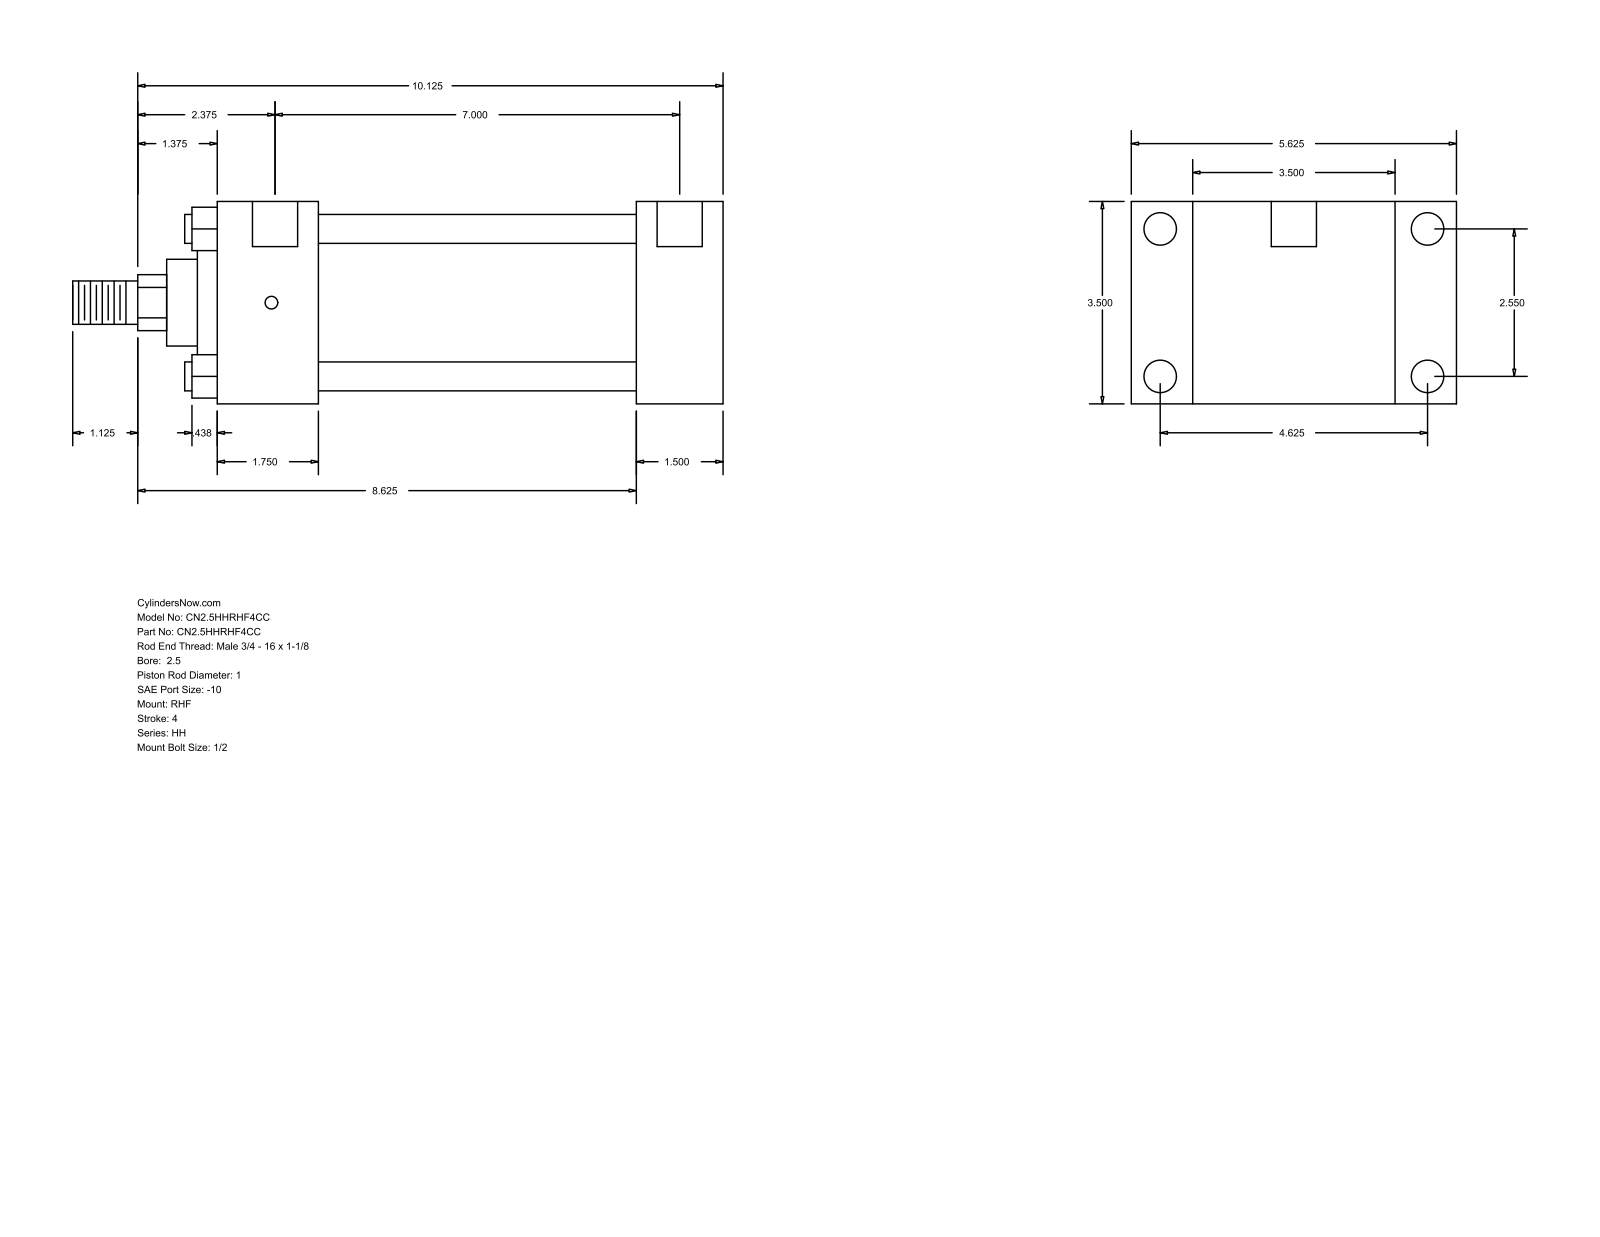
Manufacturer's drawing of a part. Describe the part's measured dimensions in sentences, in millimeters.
The part is named "HH_RHF__0250_1". Its 3-D file was written by "GSSL Pune (CONFIG_CONTROL_DESIGN)". It is 0 solids with 90 faces: 61 planar, 29 cylindrical and 0 other. Overall it measures 285.75 by 142.88 by 88.9 millimeters. Round holes: 4 of diameter 5.56, 4 of diameter 14.3, 2 of diameter 19.84. Round bosses or shafts: 4 of diameter 12.7, 1 of diameter 73.03, 1 of diameter 60.33, 1 of diameter 38.1, 1 of diameter 25.4, 1 of diameter 19.05. Partial cylindrical surfaces (rounded edges, fillets, slot ends): 1 of radius 12.29. The main face-to-face distances are 88.9, 38.11, 26.99, 115.89, 184.15, 222.26, 142.88, 44.46, 139.69, 177.8. The hole center spacings are 1.59, 64.76, 117.48, 134.15, 179.38, 180.97, 177.79.
